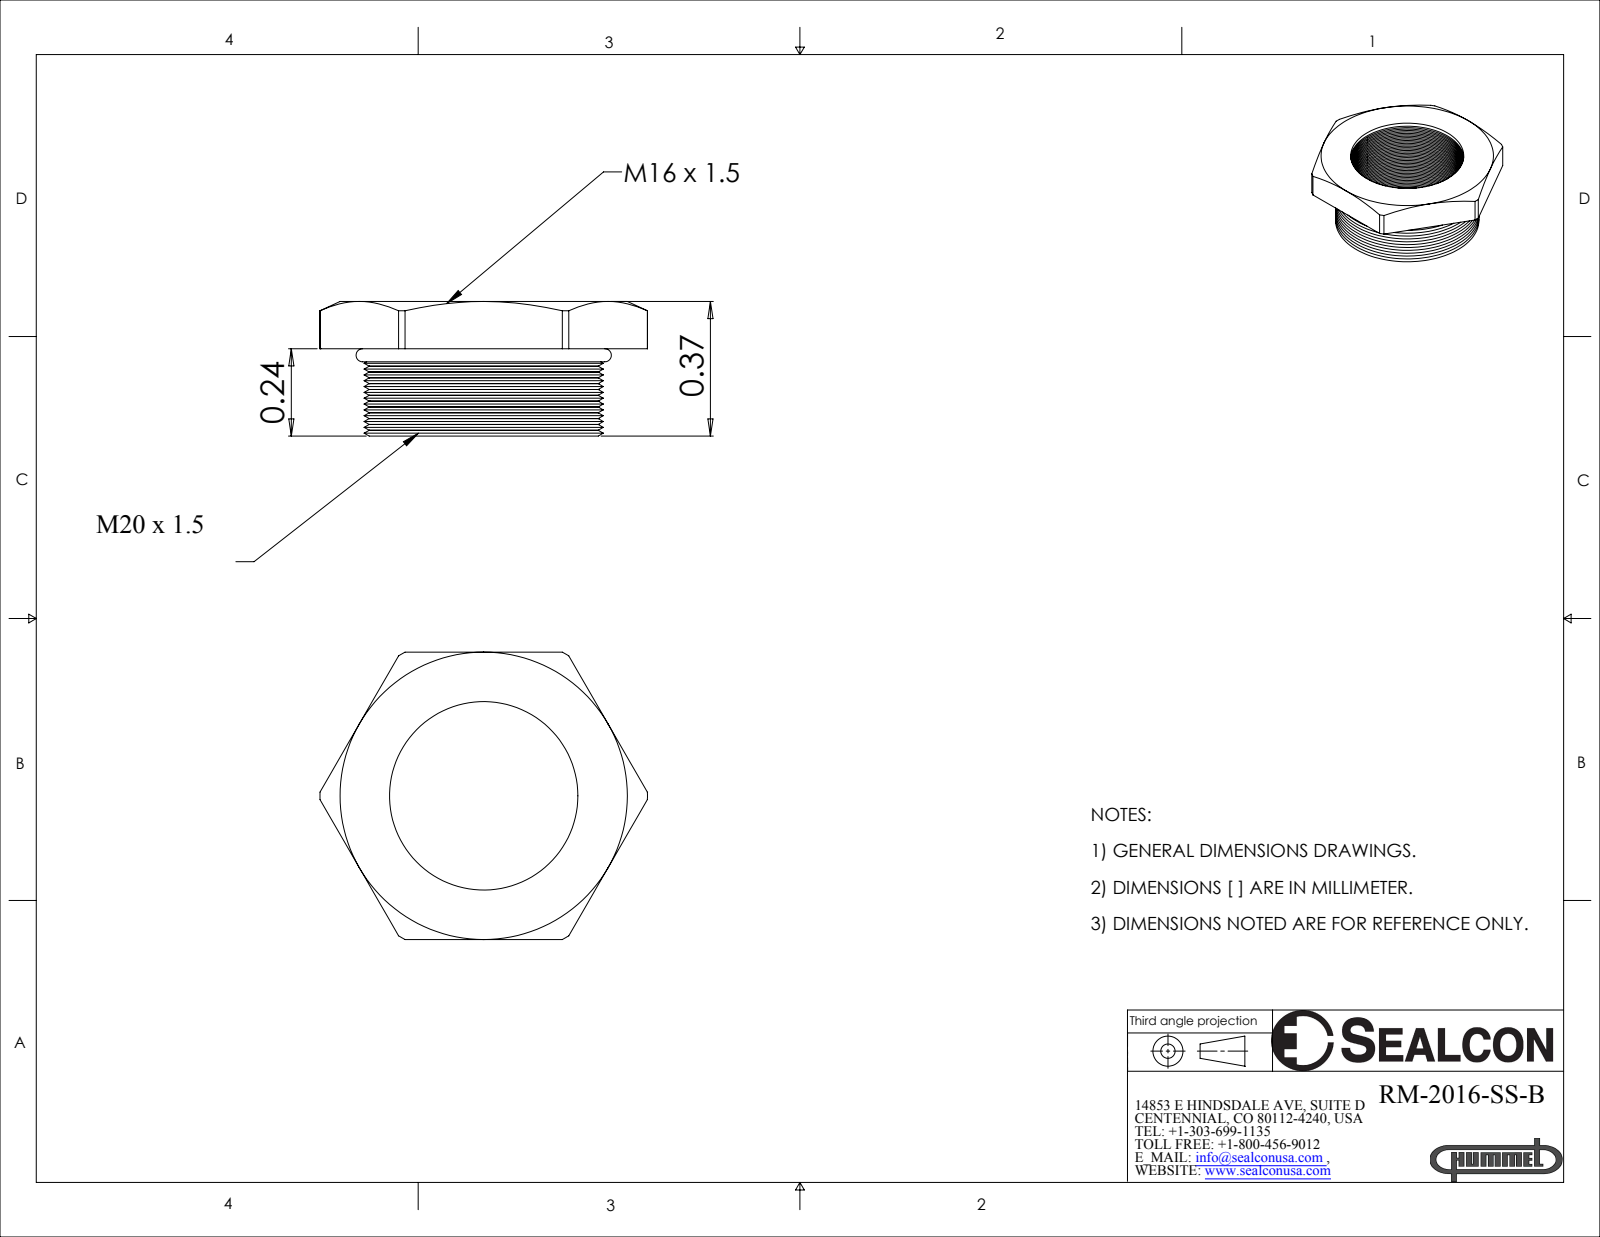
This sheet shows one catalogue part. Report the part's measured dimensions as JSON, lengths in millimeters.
{"part_name": "RM-2016-SS-B", "step_written_by": "SolidWorks 2008 (CONFIG_CONTROL_DESIGN)", "units": "millimeters", "bodies": {"solids": 2, "faces": 245, "planar": 9, "cylindrical": 81, "other": 155}, "overall_size": [22.9, 20.1, 9.4], "volume_mm3": 1100, "surface_area_mm2": 2152, "round_holes": [[13.2, 1]], "round_bosses_or_shafts": [[16, 1]], "partial_cylinders_radius": [[11.4, 1]], "face_to_face_distances": [3.3, 20.1, 6.1, 9.4]}
